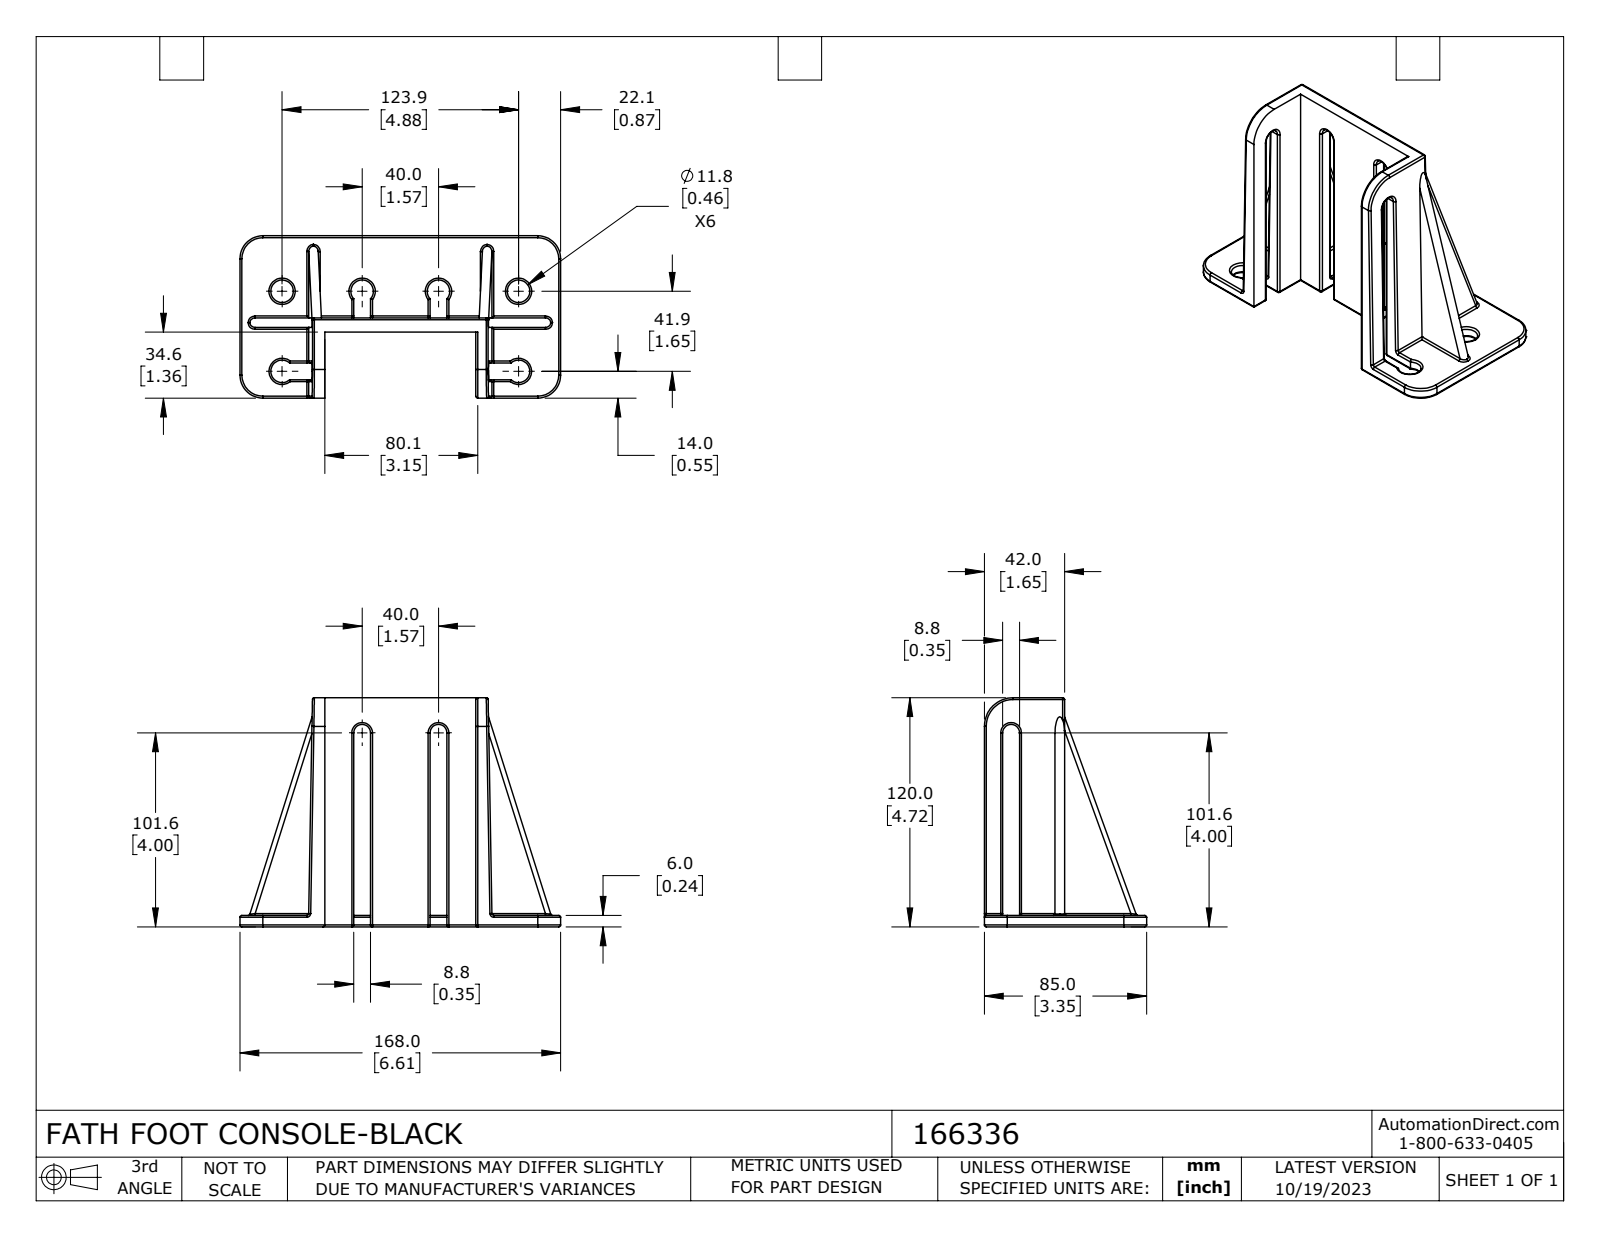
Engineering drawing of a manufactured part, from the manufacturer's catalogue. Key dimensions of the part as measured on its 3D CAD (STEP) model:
Part name (STEP PRODUCT): 166336
STEP written by: SolidWorks 2023 (CONFIG_CONTROL_DESIGN)
Units: inches
Bodies: 1 solid, 211 faces (30 planar, 102 cylindrical, 79 other)
Overall size (bounding box): 6.614 × 4.724 × 3.346
Volume: 12.61 in³ · Surface area: 115.3 in²
Round holes (diameter × count): ⌀0.465 ×2
Partial cylindrical surfaces — rounded edges, fillets, slot ends (radius × count): R0.039 ×54, R0.098 ×4, R0.232 ×4, R0.472 ×4, R0.173 ×3, R0.591 ×1
Main face-to-face distances: 0.236, 0.293, 0.197, 3.115, 0.096, 0.346, 1.36, 1.457, 1.654, 0.378
Hole centre spacings: 4.876
